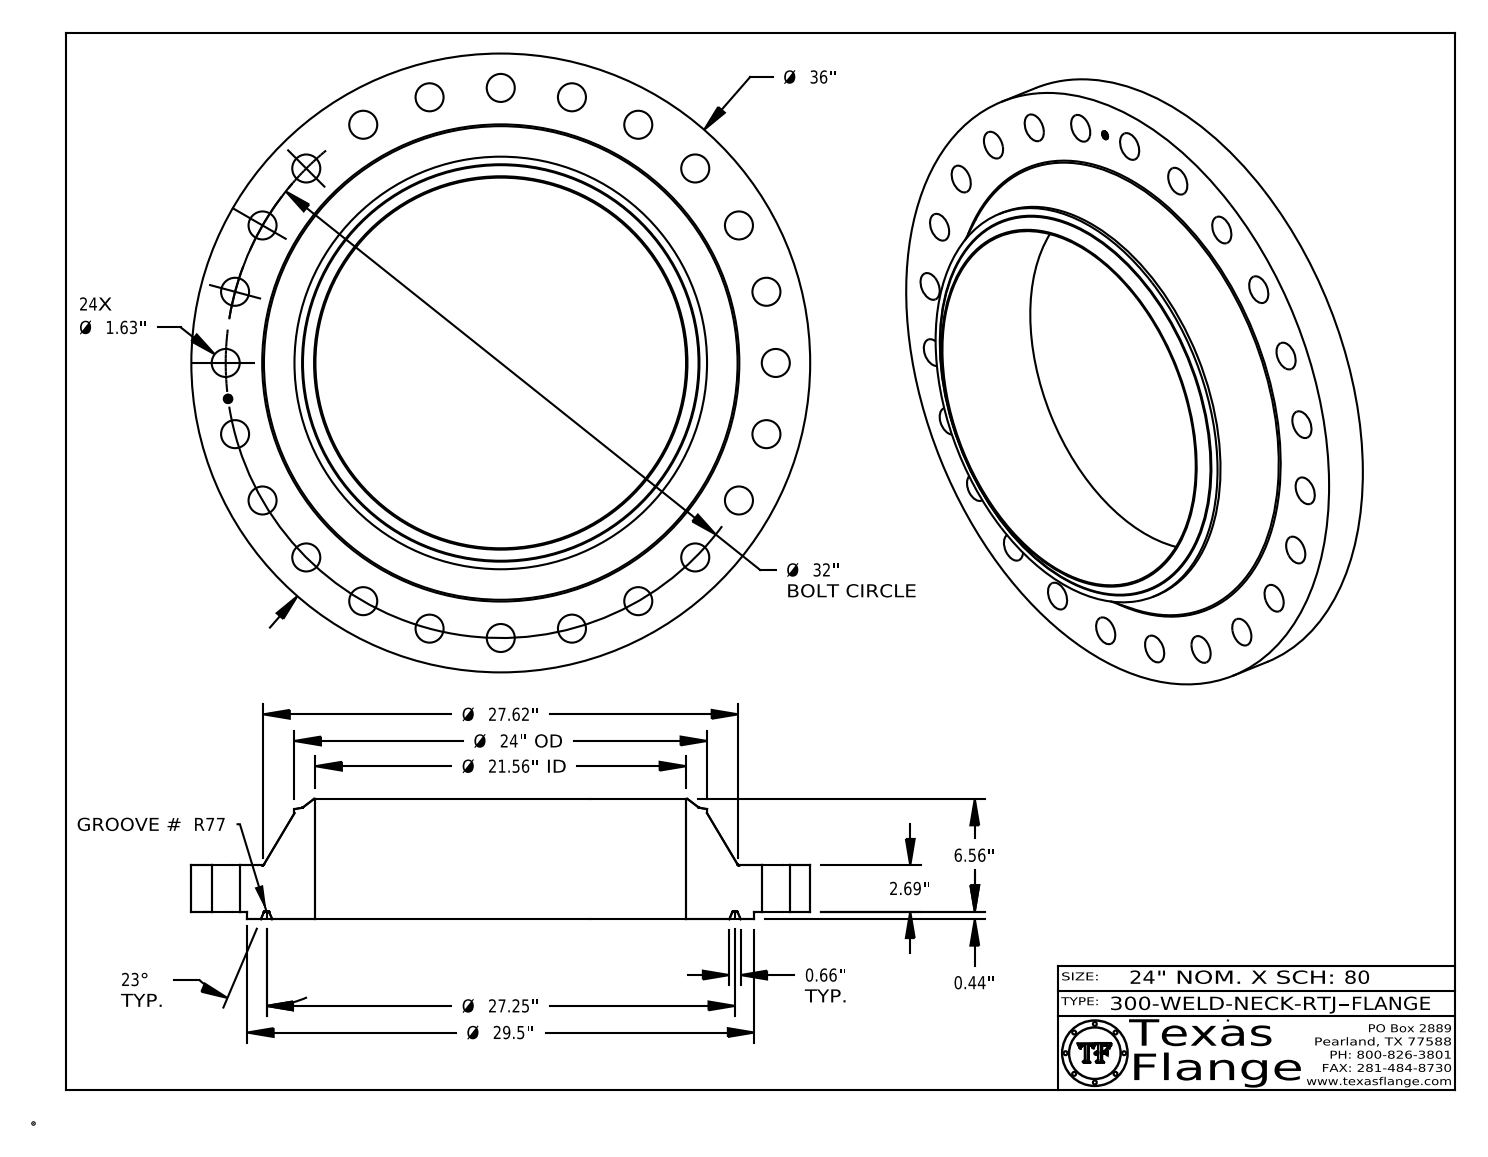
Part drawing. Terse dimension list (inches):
name: 300-WELD-NECK-RTJ
written by: CATIA V5 STEP AP214 (AUTOMOTIVE_DESIGN)
unit: in
bodies: 1 solid, 465 faces (371 planar, 76 cylindrical, 18 other)
size: 36 × 36 × 6.998
volume: 2 267 in³; area: 2 572 in²
holes: 24× ⌀1.63, 1× ⌀0.495, 1× ⌀21.562
bosses: 8× ⌀0.03, 1× ⌀36, 1× ⌀29.5, 1× ⌀24, 1× ⌀0.39
face distances: 2.69, 0.438, 3.128, 6.998, 6.56, 3.87, 3.113, 2.675, 0.015, 3.885
hole spacings: 16, 30.909, 4.177, 8.282, 12.246, 19.48, 22.627, 25.387
